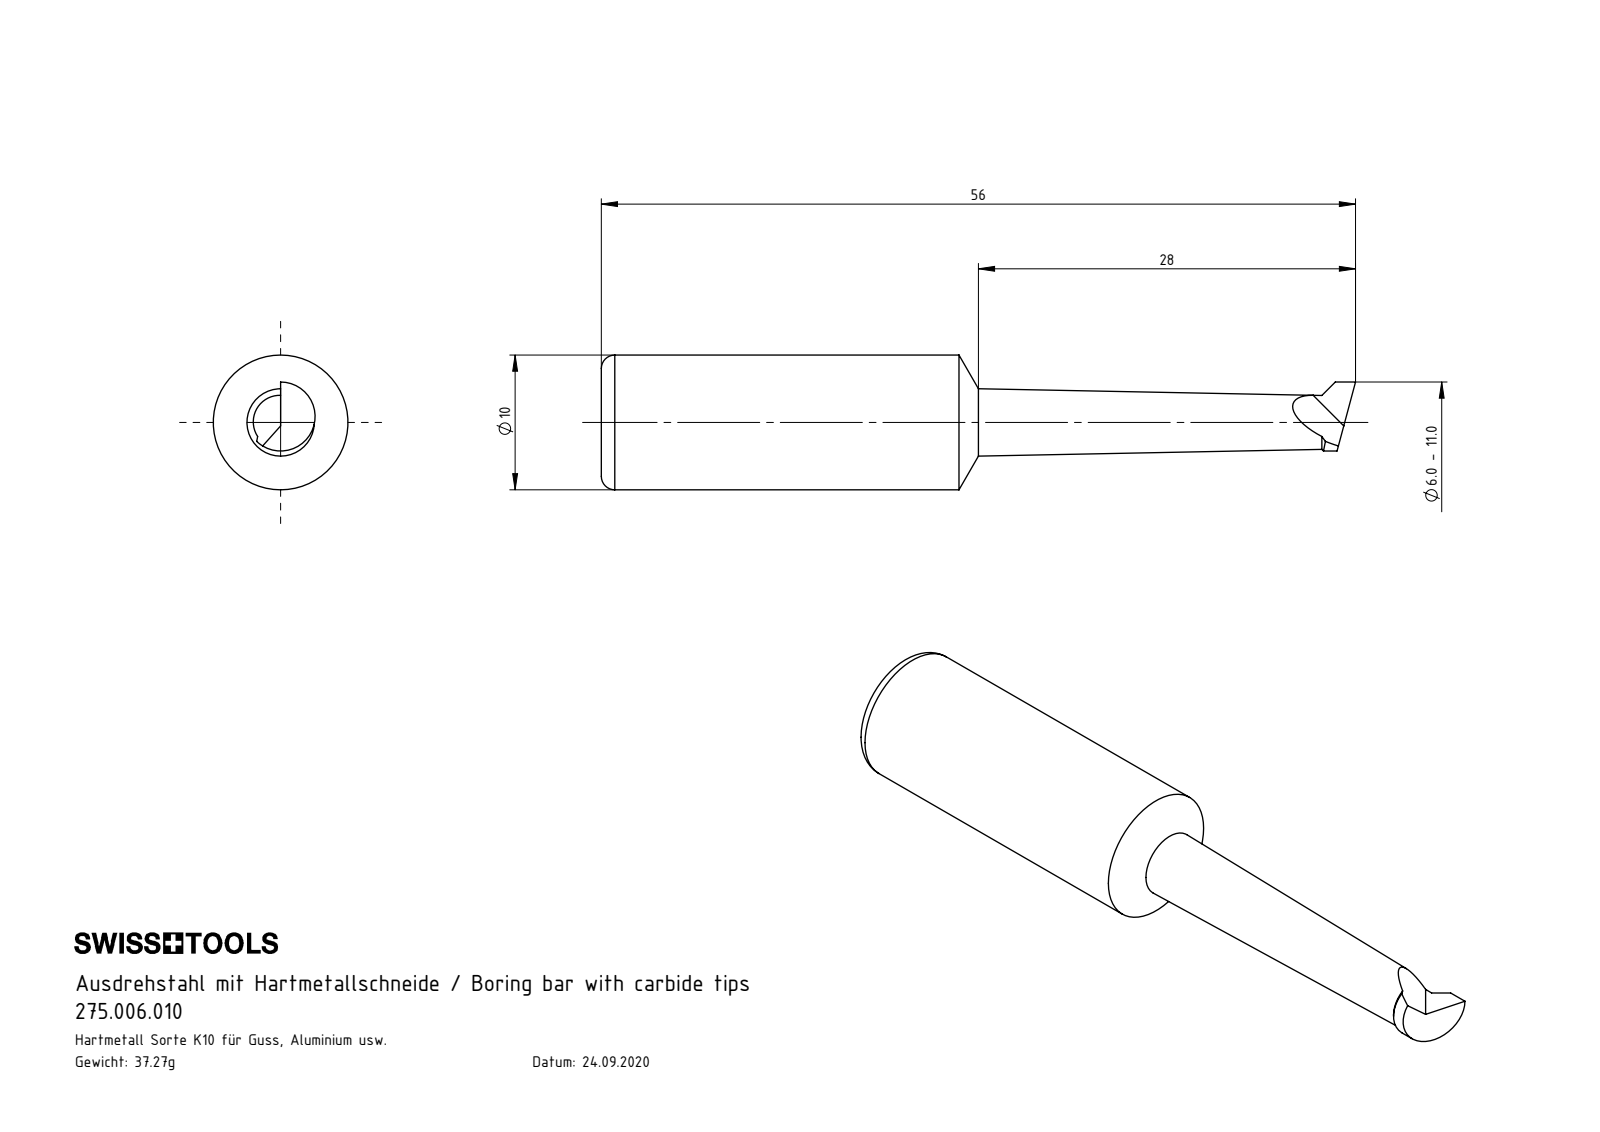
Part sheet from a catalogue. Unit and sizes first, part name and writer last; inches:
Units: inches
Overall size (bounding box): 2.205 × 0.394 × 0.394
Round bosses / shafts (diameter × count): ⌀0.394 ×1
Partial cylindrical surfaces — rounded edges, fillets, slot ends (radius × count): R0.101 ×1
Volume: 0.157 in³ · Surface area: 2.119 in²
Bodies: 1 solid, 14 faces (4 planar, 3 cylindrical, 7 other)
Part name (STEP PRODUCT): 275.006.010
STEP written by: SolidWorks 2022 (AUTOMOTIVE_DESIGN)
